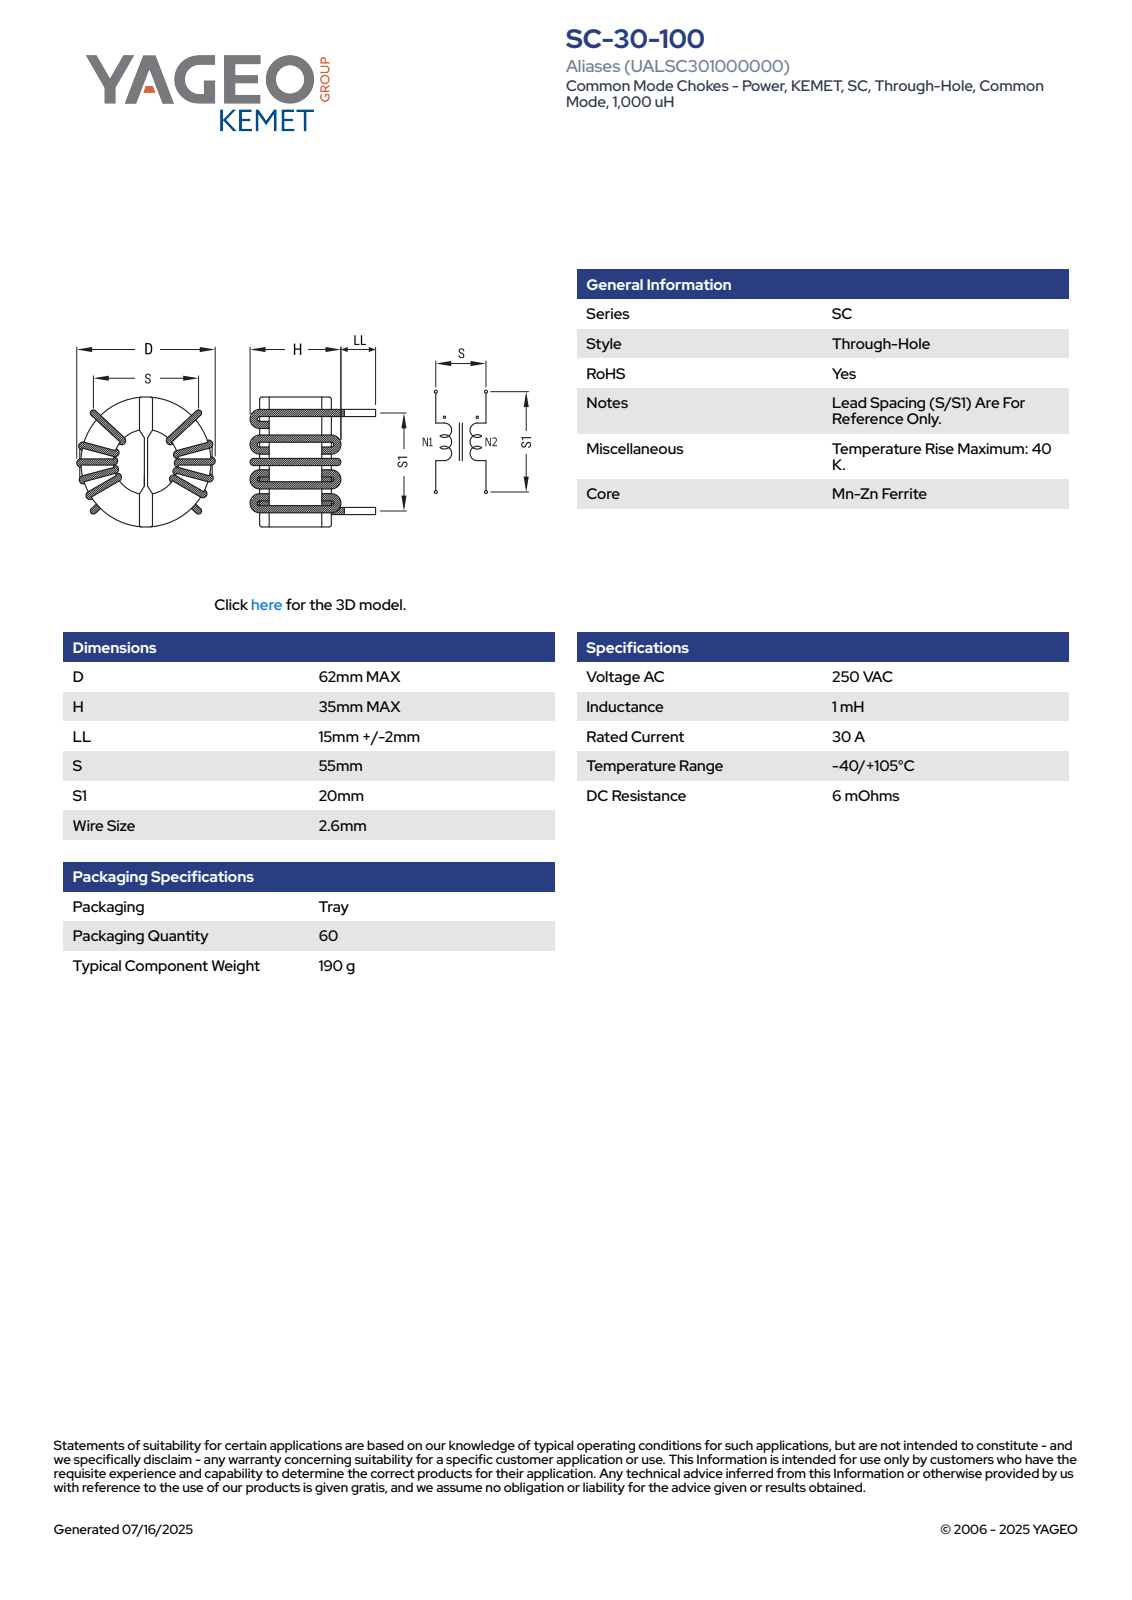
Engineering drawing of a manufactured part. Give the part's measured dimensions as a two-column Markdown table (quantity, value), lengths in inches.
| quantity | value |
| --- | --- |
| part name | SC-30-100 |
| STEP written by | SolidWorks 2018 (AUTOMOTIVE_DESIGN) |
| units | inches |
| bodies | 1 solid, 342 faces (141 planar, 93 cylindrical, 108 other) |
| overall size | 2.441 × 2.43 × 1.969 |
| volume | 4.413 in³ |
| surface area | 27.35 in² |
| round holes (diameter × count) | 0.665 × 1 |
| round bosses / shafts (diameter × count) | 0.102 × 8, 2.441 × 1 |
| partial cylindrical surfaces (radius × count) | 0.051 × 34, 0.059 × 2, 0.518 × 1, 0.541 × 1, 0.925 × 1, 0.933 × 1, 0.969 × 1 |
| main face-to-face distances | 1.035, 0.047, 0.079, 0.031, 0.126, 0.171, 1.207, 0.045, 0.081, 0.033 |
